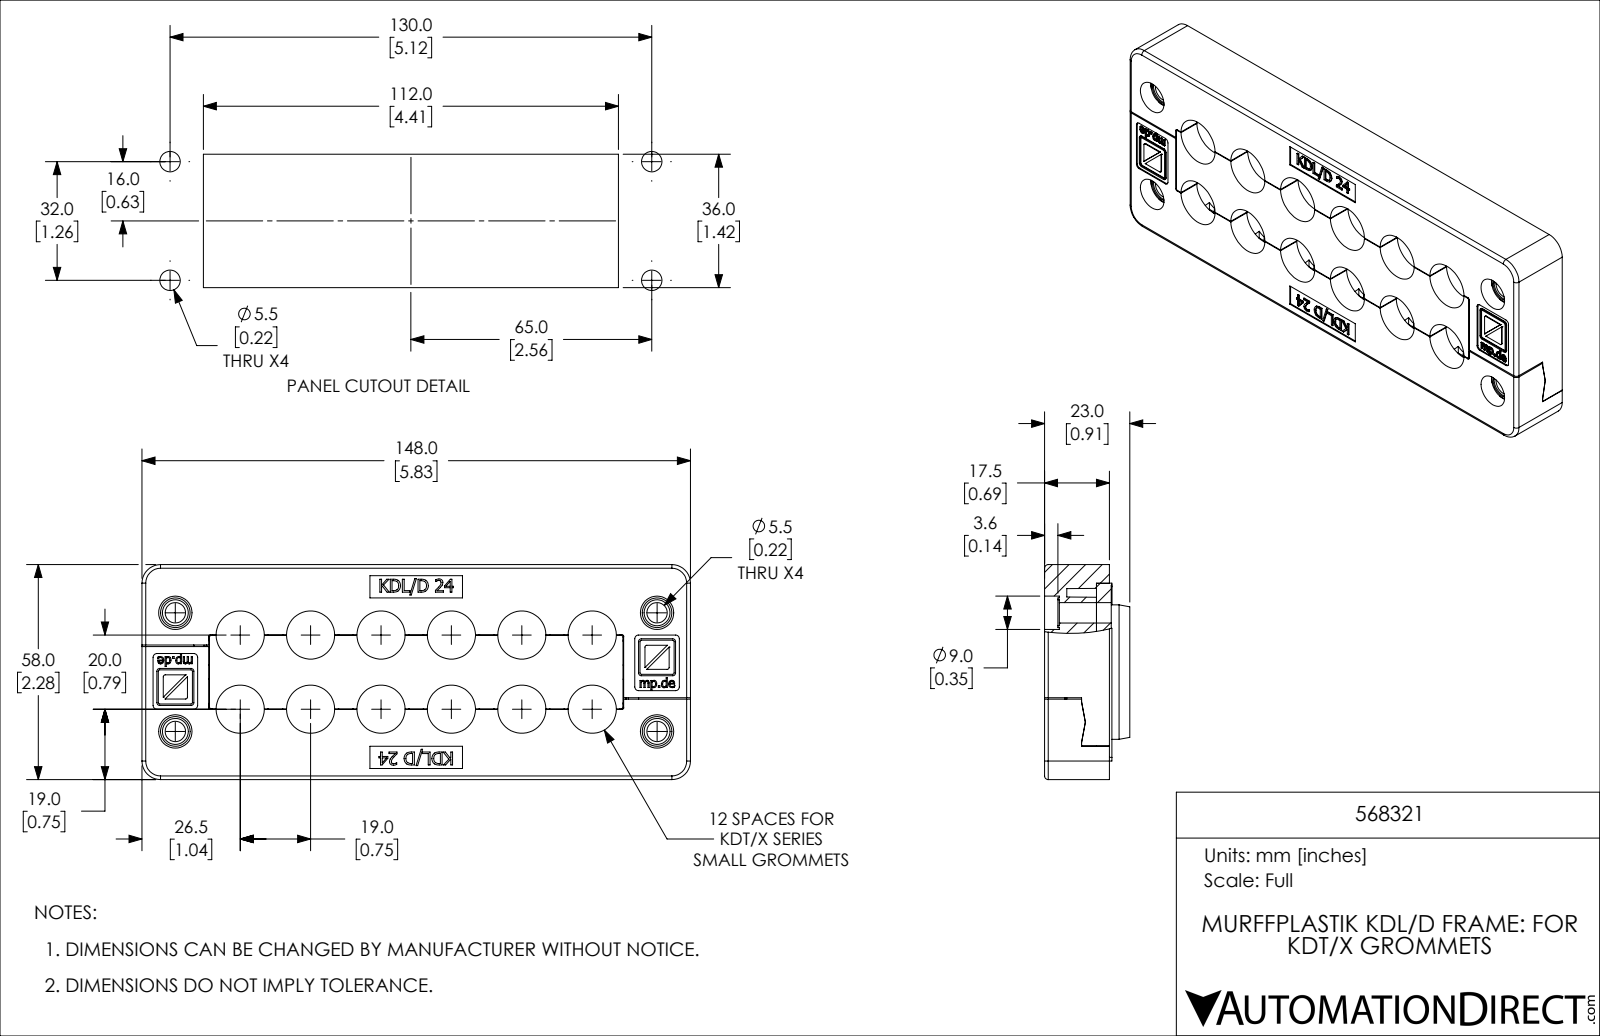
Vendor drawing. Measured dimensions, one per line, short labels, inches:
name: 568321
written by: SolidWorks 2019 (CONFIG_CONTROL_DESIGN)
unit: in
bodies: 4 solids, 1737 faces (1037 planar, 307 cylindrical, 393 other)
size: 5.827 × 2.283 × 0.906
volume: 6.666 in³; area: 93.93 in²
holes: 12× ⌀0.512, 10× ⌀0.596, 6× ⌀0.197, 4× ⌀0.217, 4× ⌀0.276, 4× ⌀0.354, 2× ⌀0.236, 2× ⌀0.591
bosses: 4× ⌀0.315
rounds: 32× R0.02, 26× R0.039, 12× R0.016, 8× R0.031, 4× R0.004, 4× R0.006, 4× R0.012, 4× R0.197
face distances: 0.197, 0.157, 0.551, 0.02, 0.236, 0.138, 0.453, 2.283, 0.669, 0.689
hole spacings: 0.748, 1.086, 1.496, 1.691, 0.787, 2.244, 2.378, 2.992
